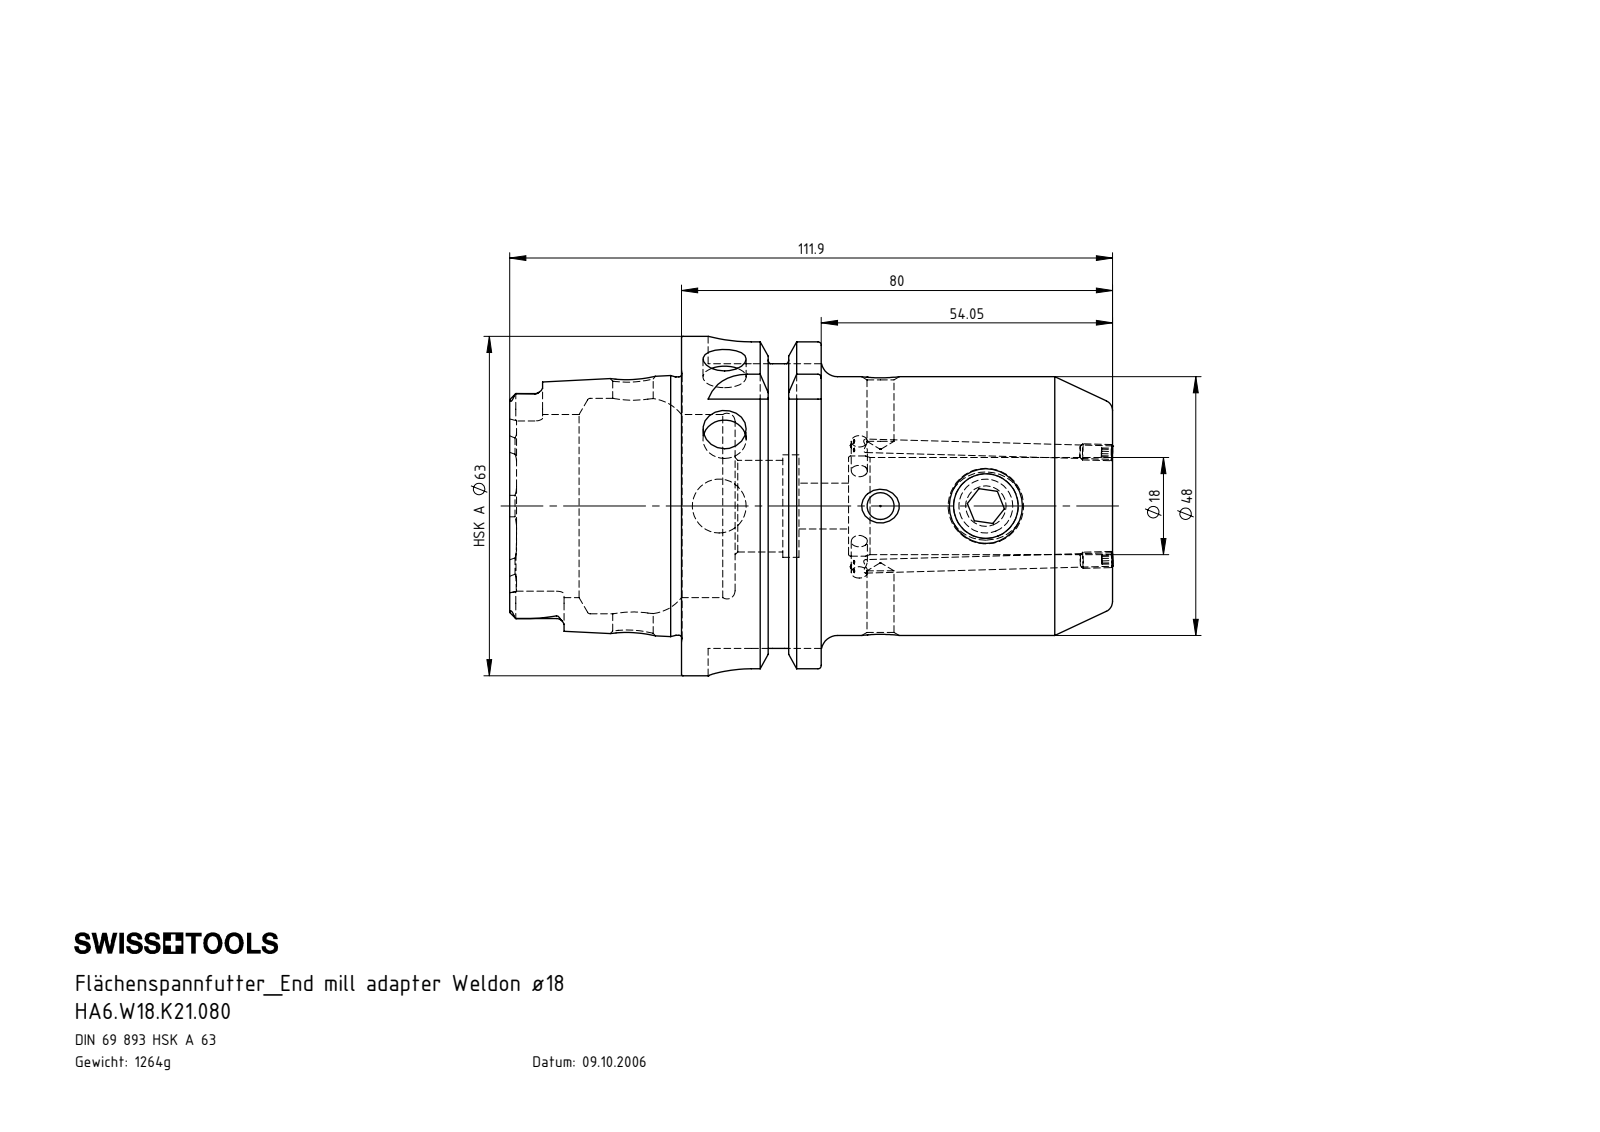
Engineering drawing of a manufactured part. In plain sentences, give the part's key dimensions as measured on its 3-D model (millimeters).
The part is named "HA6.W18.K21.080; ERU-CJ2.001.006; W16-ER1.001.016; HA6-W18.K21.080_B_Fertigbearbeitung". Its 3-D file was written by "SolidWorks 2012 (CONFIG_CONTROL_DESIGN)". It is 4 solids with 292 faces: 78 planar, 86 cylindrical and 128 other. Overall it measures 111.98 by 63 by 63 millimeters. Its volume is 160 954 cubic millimeters and its surface area 35 801 square millimeters. Round holes: 2 of diameter 2.5, 2 of diameter 5, 2 of diameter 8, 1 of diameter 3, 1 of diameter 7.5, 1 of diameter 8.5, 1 of diameter 10, 1 of diameter 12, 1 of diameter 17, 1 of diameter 18, 1 of diameter 18.6, 1 of diameter 19. Round bosses or shafts: 2 of diameter 3, 1 of diameter 63, 1 of diameter 54.95, 1 of diameter 48, 1 of diameter 47.94, 1 of diameter 14. Partial cylindrical surfaces (rounded edges, fillets, slot ends): 6 of radius 1.4, 4 of radius 2.88, 4 of radius 8, 1 of radius 10.56. The main face-to-face distances are 80, 25.95, 54.05, 16, 9.95, 70.05, 52.8, 31.9, 41.85, 57.85. The hole center spacings are 19.55, 29.95, 45.95, 49.5.
